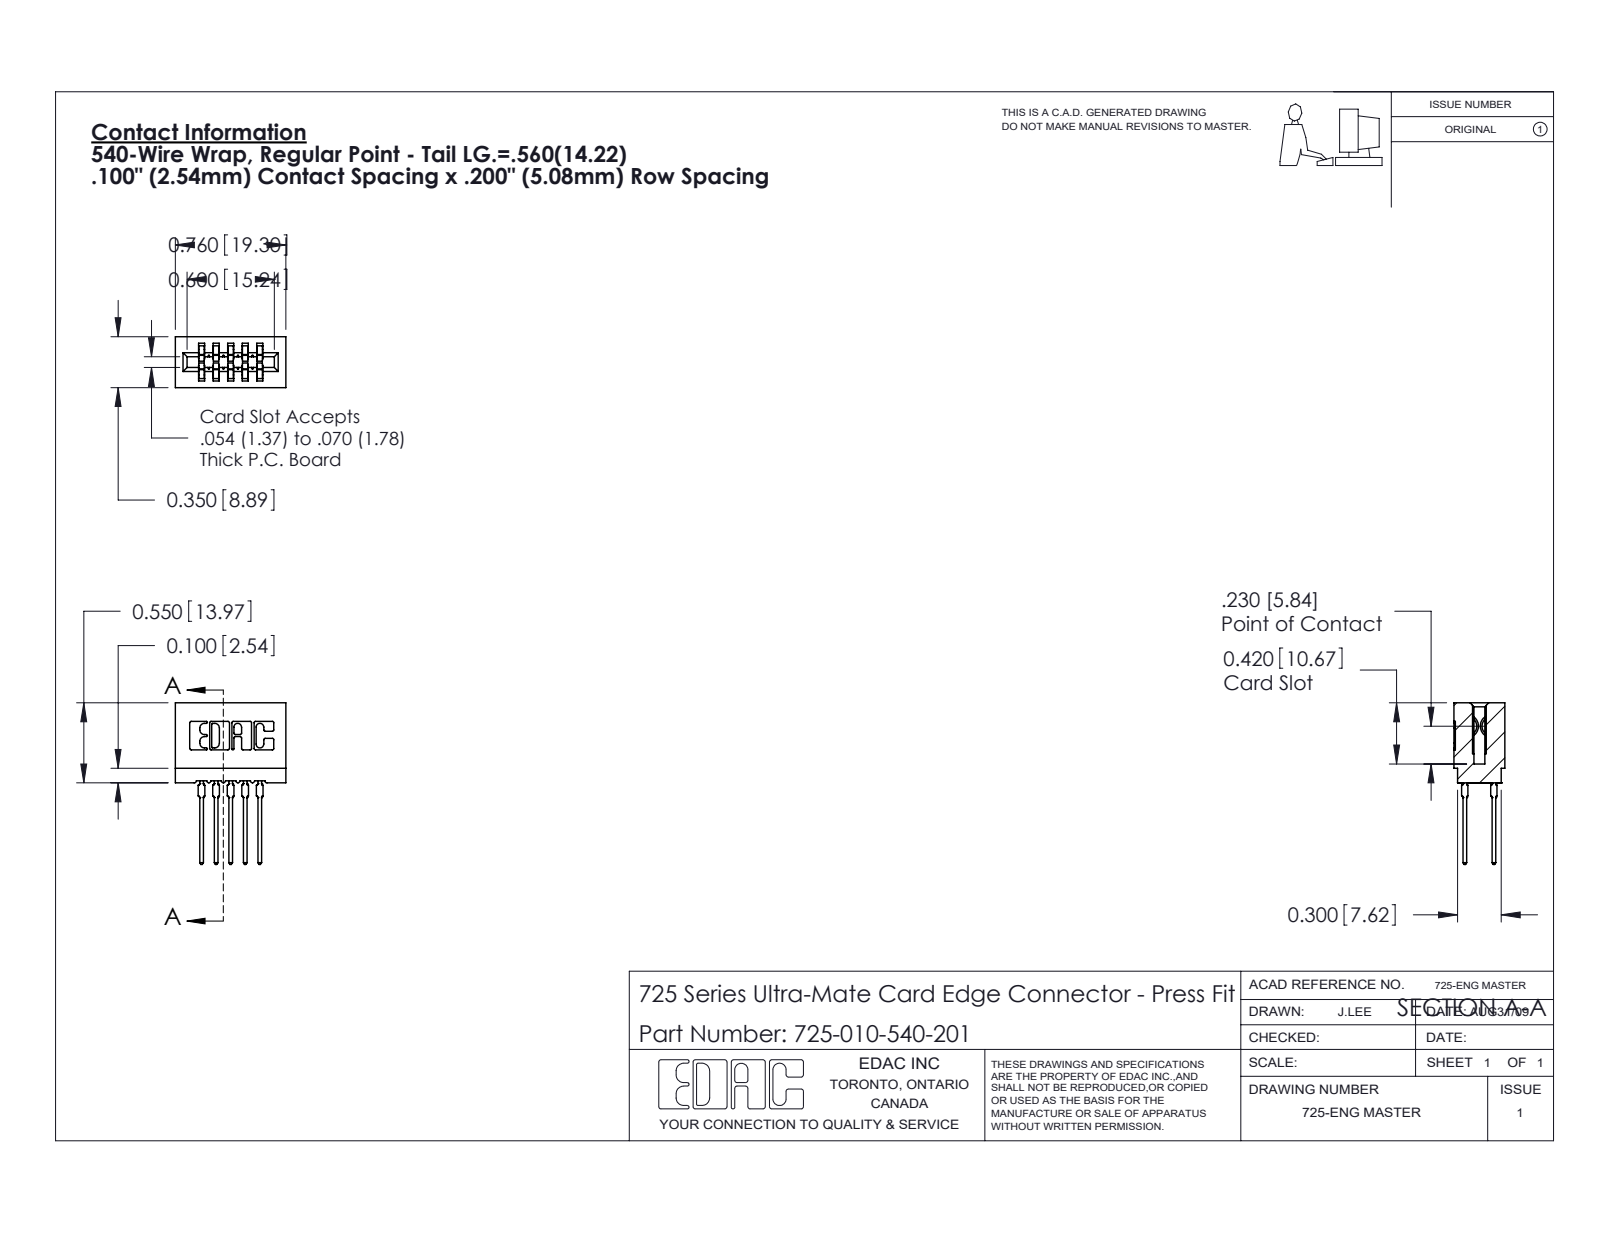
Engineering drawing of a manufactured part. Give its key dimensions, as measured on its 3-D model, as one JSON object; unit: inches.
{"part_name": "725 Part_Insulator Option - 01; 725-010-540-201; 745-292-001_540", "step_written_by": "SolidWorks 2020 (CONFIG_CONTROL_DESIGN)", "units": "inches", "bodies": {"solids": 11, "faces": 990, "planar": 515, "cylindrical": 215, "other": 260}, "overall_size": [1.111, 0.76, 0.35], "volume_in3": 0.107, "surface_area_in2": 4.672, "partial_cylinders_radius": [[0.01, 22], [0.021, 20], [0.015, 10], [0.005, 8], [0.011, 8], [0.007, 6], [0.031, 6], [0.026, 3]], "face_to_face_distances": [0.1, 0.2, 0.042, 0.3, 0.142, 0.058, 0.287, 0.063, 0.242, 0.158]}
